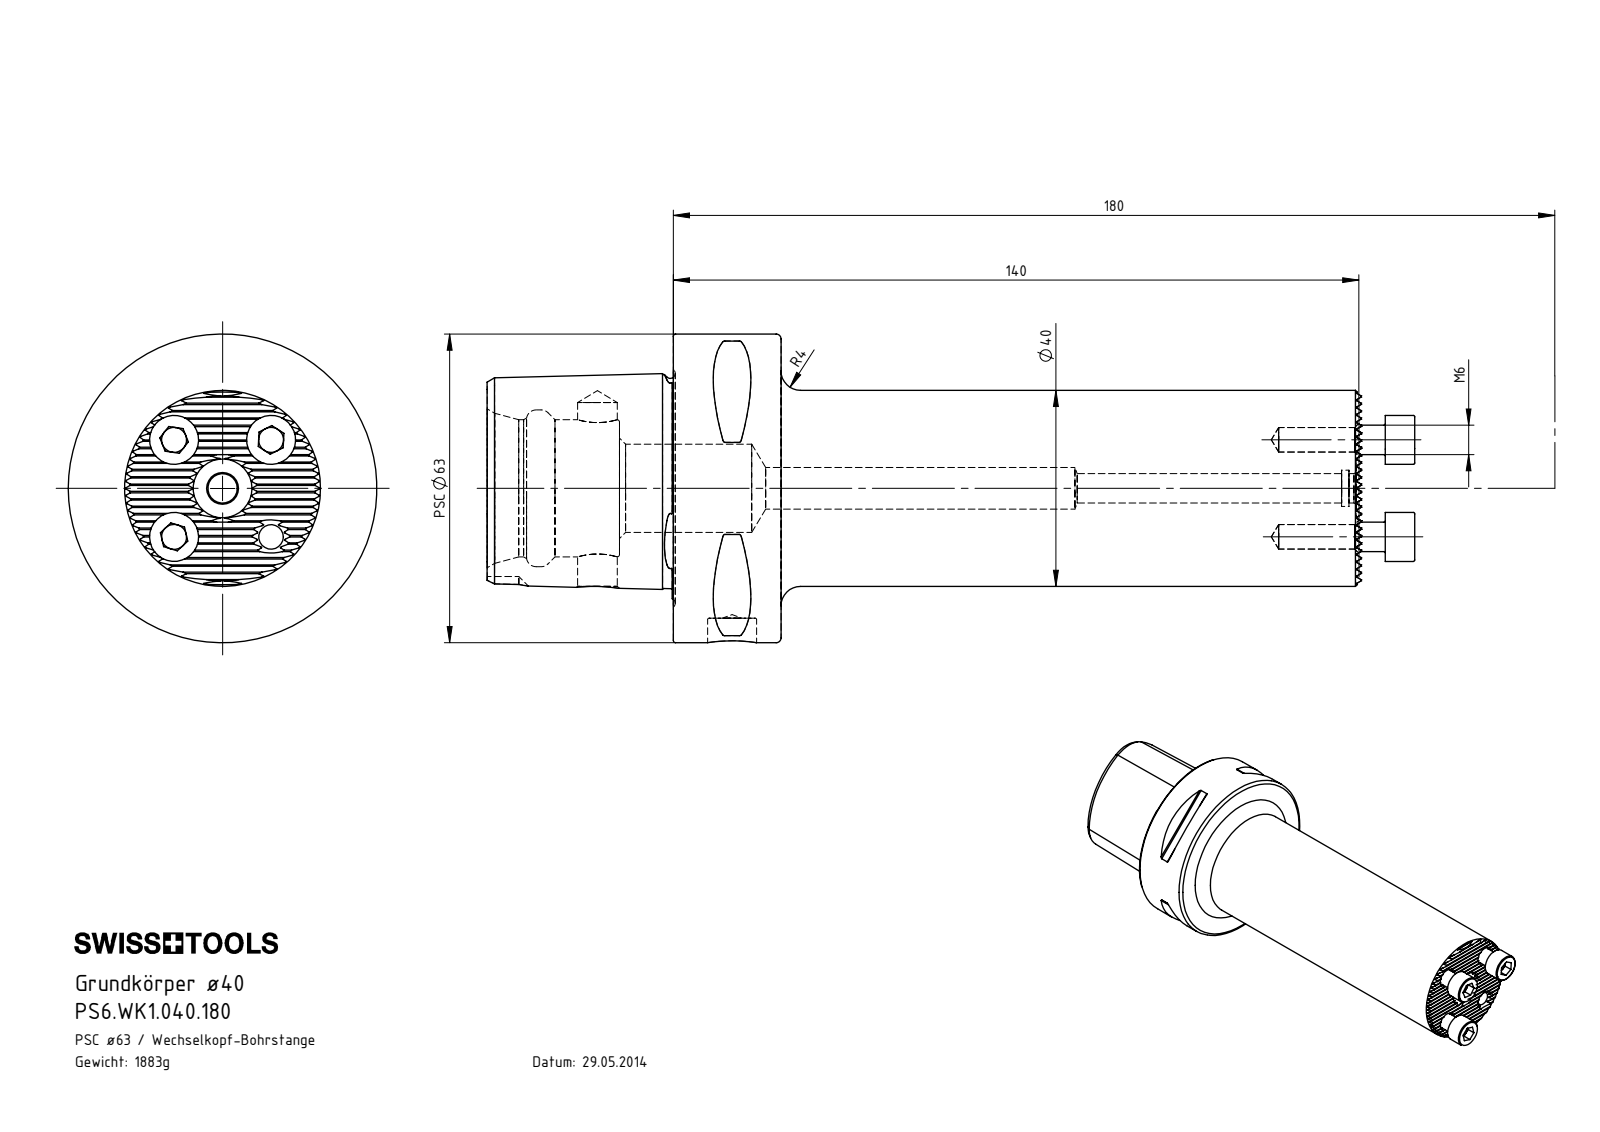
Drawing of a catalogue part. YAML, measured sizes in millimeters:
part_name: "PS6.WK1.040.180; DIN 3771 - 6x1; PS6-WK1.040.180_B; ISO 4762 - M6 x 16"
step_written_by: "SolidWorks 2017 (AUTOMOTIVE_DESIGN)"
units: millimeters
bodies: {solids: 5, faces: 461, planar: 227, cylindrical: 107, other: 127}
overall_size: [189.4, 63, 63]
volume: 240153
surface_area: 41009
round_holes:
  - {diameter: 5, count: 4}
  - {diameter: 4, count: 1}
  - {diameter: 6, count: 1}
  - {diameter: 7.4, count: 1}
  - {diameter: 8.1, count: 1}
  - {diameter: 8.5, count: 1}
  - {diameter: 18, count: 1}
  - {diameter: 28, count: 1}
  - {diameter: 32, count: 1}
round_bosses_or_shafts:
  - {diameter: 10, count: 3}
  - {diameter: 6, count: 3}
  - {diameter: 63, count: 1}
  - {diameter: 40, count: 1}
partial_cylinders:
  - {radius: 0.12, count: 27}
  - {radius: 0.5, count: 8}
  - {radius: 6, count: 1}
face_to_face_distances: [22, 1.3, 2.6, 3.9, 5.2, 12.99, 11, 38, 60, 9.09]
hole_center_spacings: [14, 19.8, 28, 27.5]
